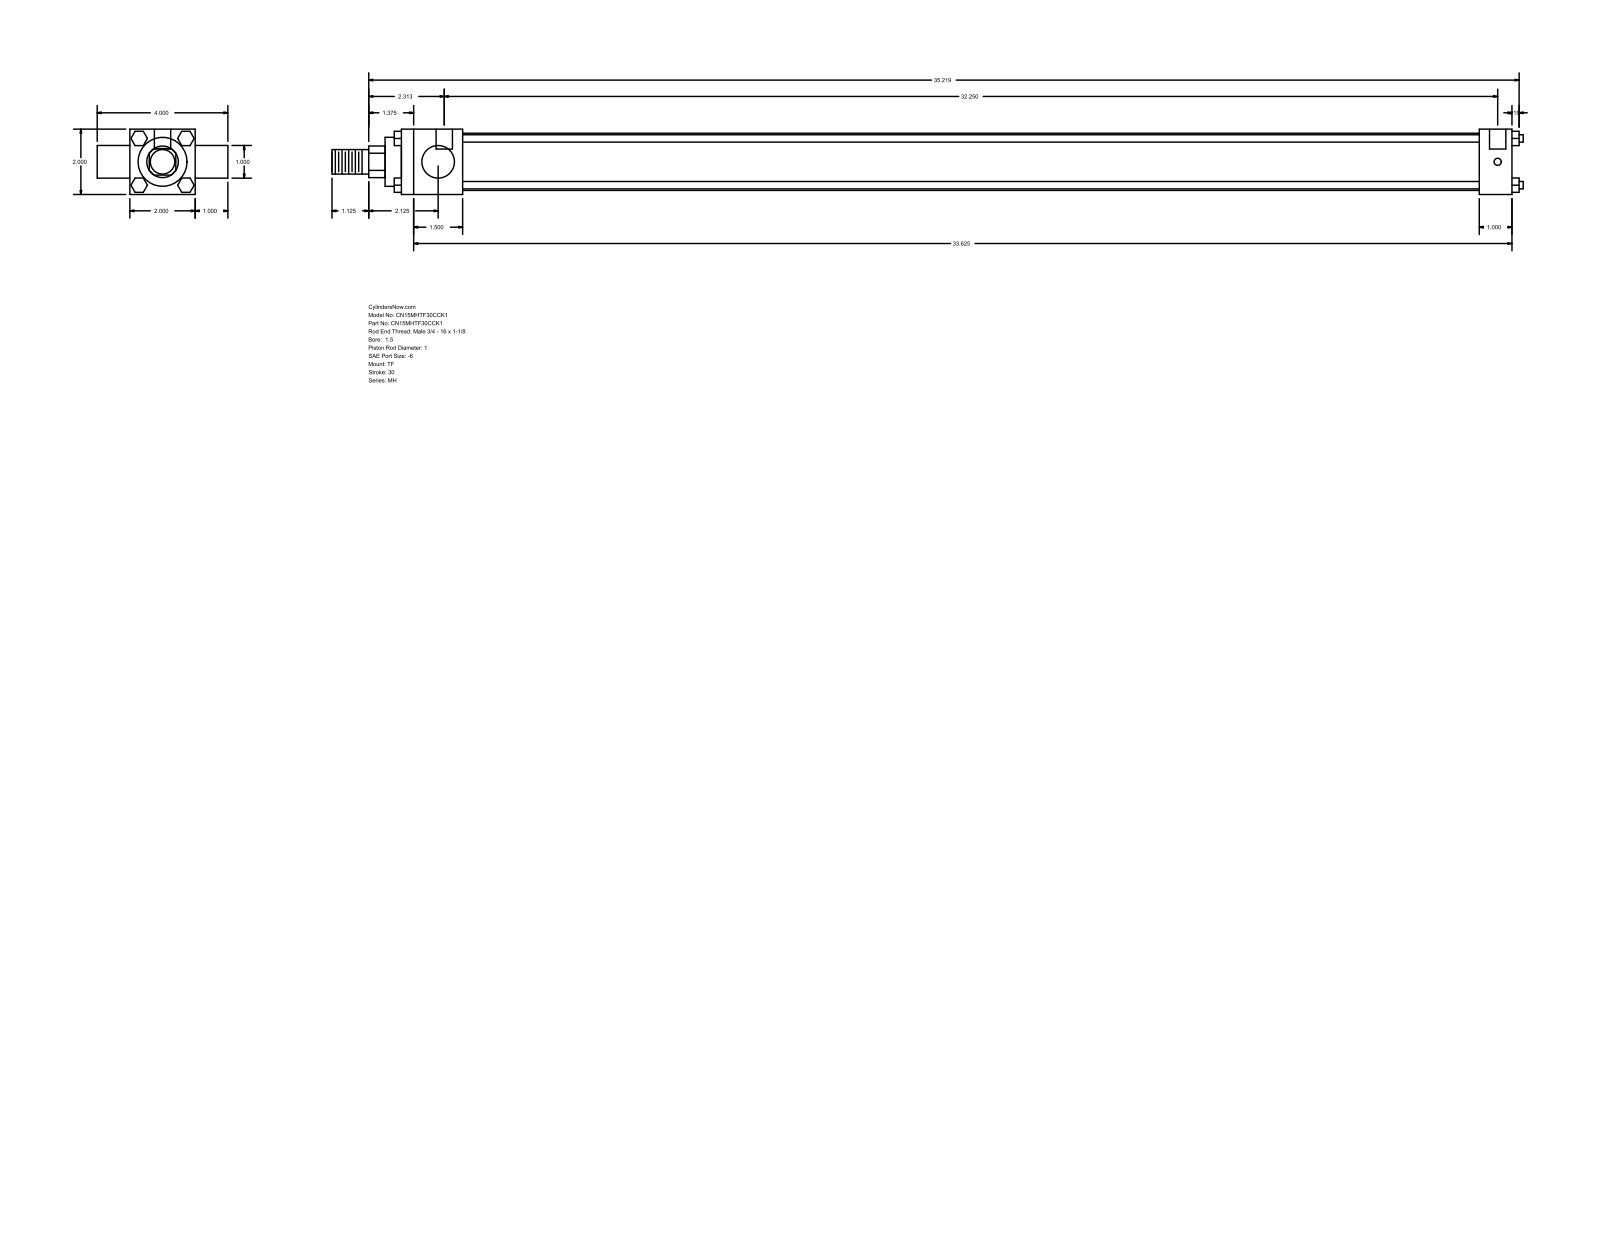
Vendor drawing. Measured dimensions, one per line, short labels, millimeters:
name: MH_TF__0150_1
written by: GSSL Pune (CONFIG_CONTROL_DESIGN)
unit: mm
bodies: 0 solids, 120 faces (92 planar, 28 cylindrical, 0 other)
size: 926.31 × 101.6 × 50.8
holes: 3× ⌀5.56, 2× ⌀12.7
bosses: 4× ⌀5.71, 2× ⌀25.4, 1× ⌀44.45, 1× ⌀38.1, 1× ⌀19.05
rounds: 1× R12.29
face distances: 50.8, 25.4, 863.6, 76.2, 47.63, 815.97, 838.2, 790.57, 101.6, 12.7
hole spacings: 3.18, 819.15, 822.33
